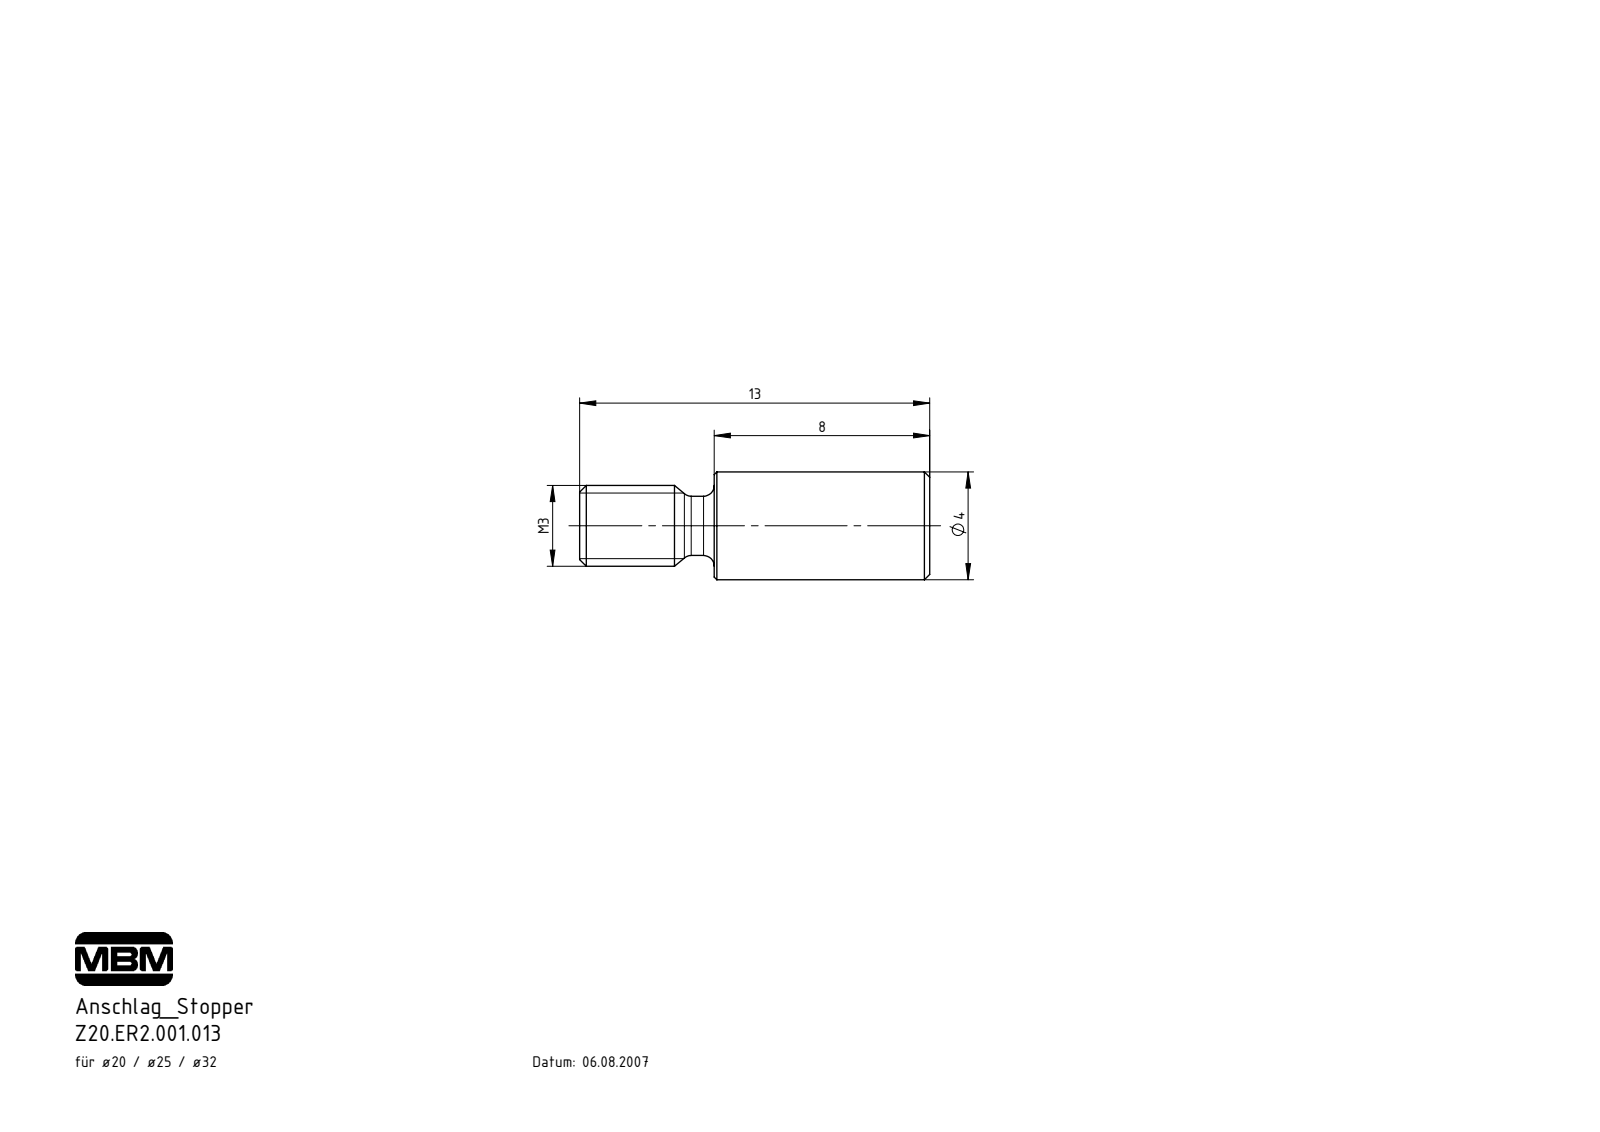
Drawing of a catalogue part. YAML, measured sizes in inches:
part_name: "Z20.ER2.001.013"
step_written_by: "SolidWorks 2017 (AUTOMOTIVE_DESIGN)"
units: inches
bodies: {solids: 1, faces: 39, planar: 15, cylindrical: 8, other: 16}
overall_size: [0.512, 0.157, 0.157]
volume: 0.007
surface_area: 0.293
round_holes:
  - {diameter: 0.079, count: 1}
round_bosses_or_shafts:
  - {diameter: 0.157, count: 1}
  - {diameter: 0.118, count: 1}
  - {diameter: 0.087, count: 1}
face_to_face_distances: [0.079, 0.512, 0.197, 0.315, 0.433, 0.236]
